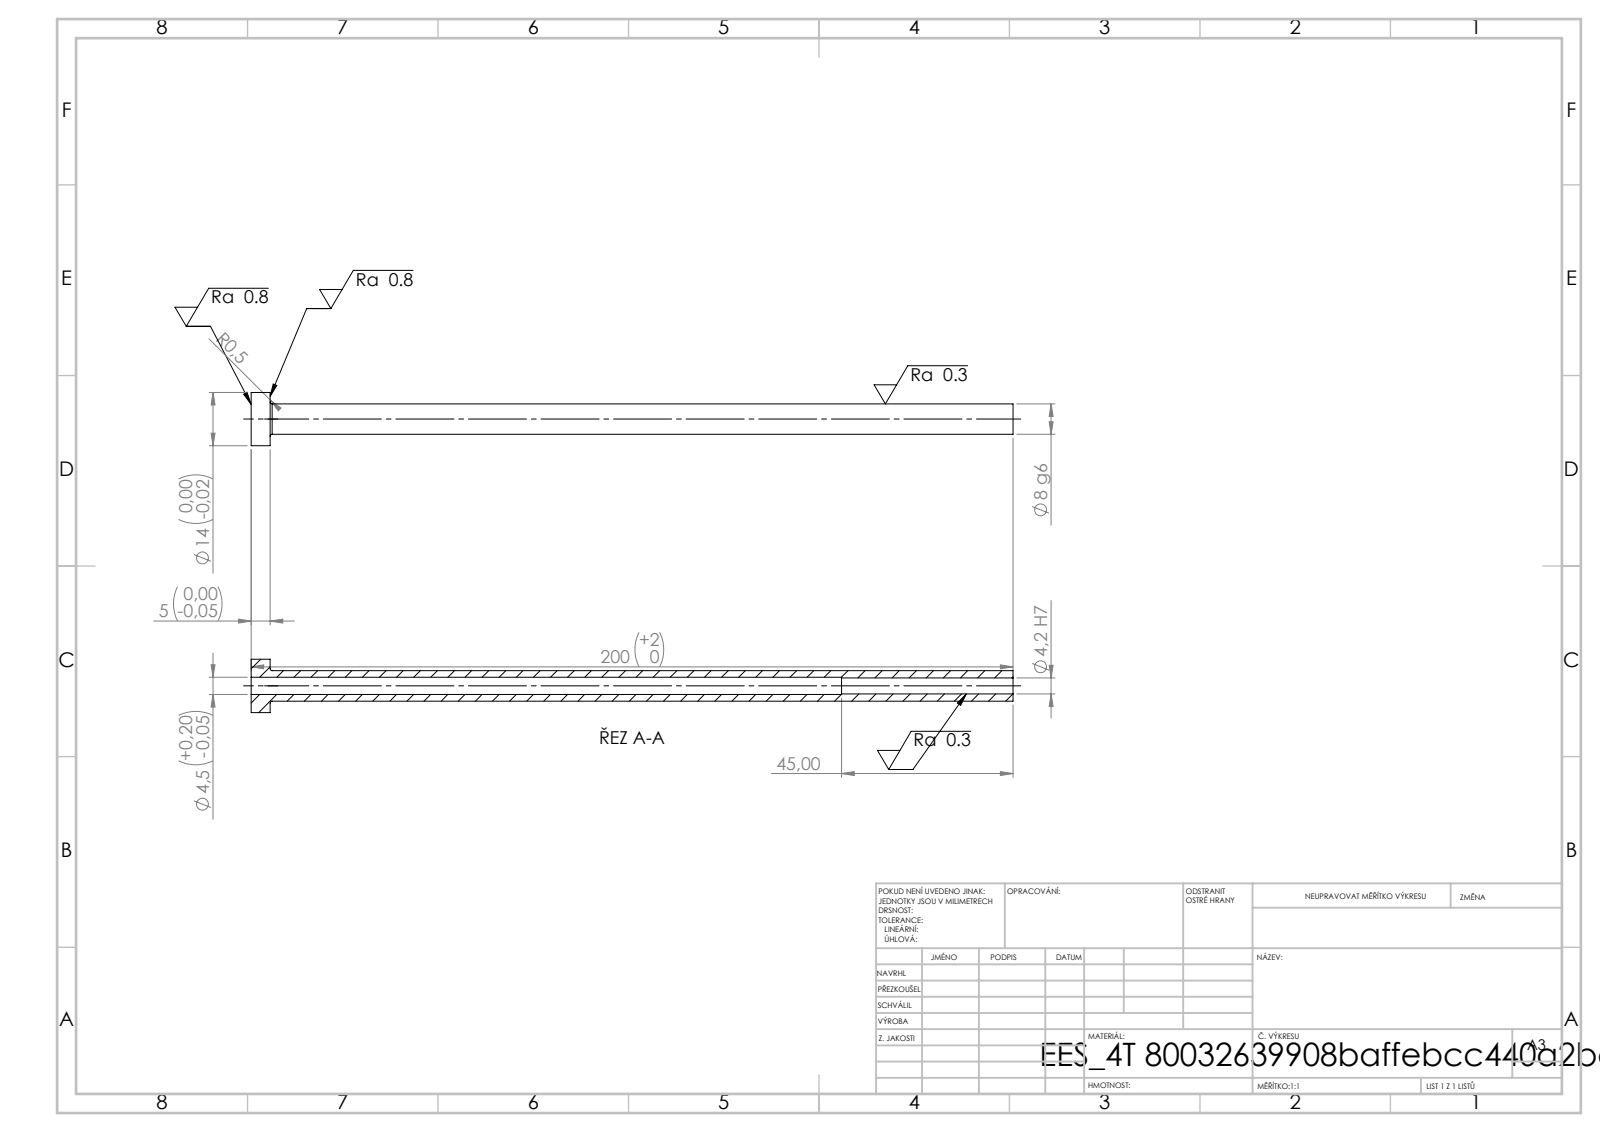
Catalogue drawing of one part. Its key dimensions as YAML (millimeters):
step_written_by: "SolidWorks 2019 (CONFIG_CONTROL_DESIGN)"
units: millimeters
bodies: {solids: 1, faces: 14, planar: 4, cylindrical: 8, other: 2}
overall_size: [200, 14, 14]
volume: 7484
surface_area: 8181
round_holes:
  - {diameter: 4.2, count: 1}
  - {diameter: 4.5, count: 1}
round_bosses_or_shafts:
  - {diameter: 14, count: 1}
  - {diameter: 8, count: 1}
face_to_face_distances: [5, 200, 195, 155, 150, 45]
